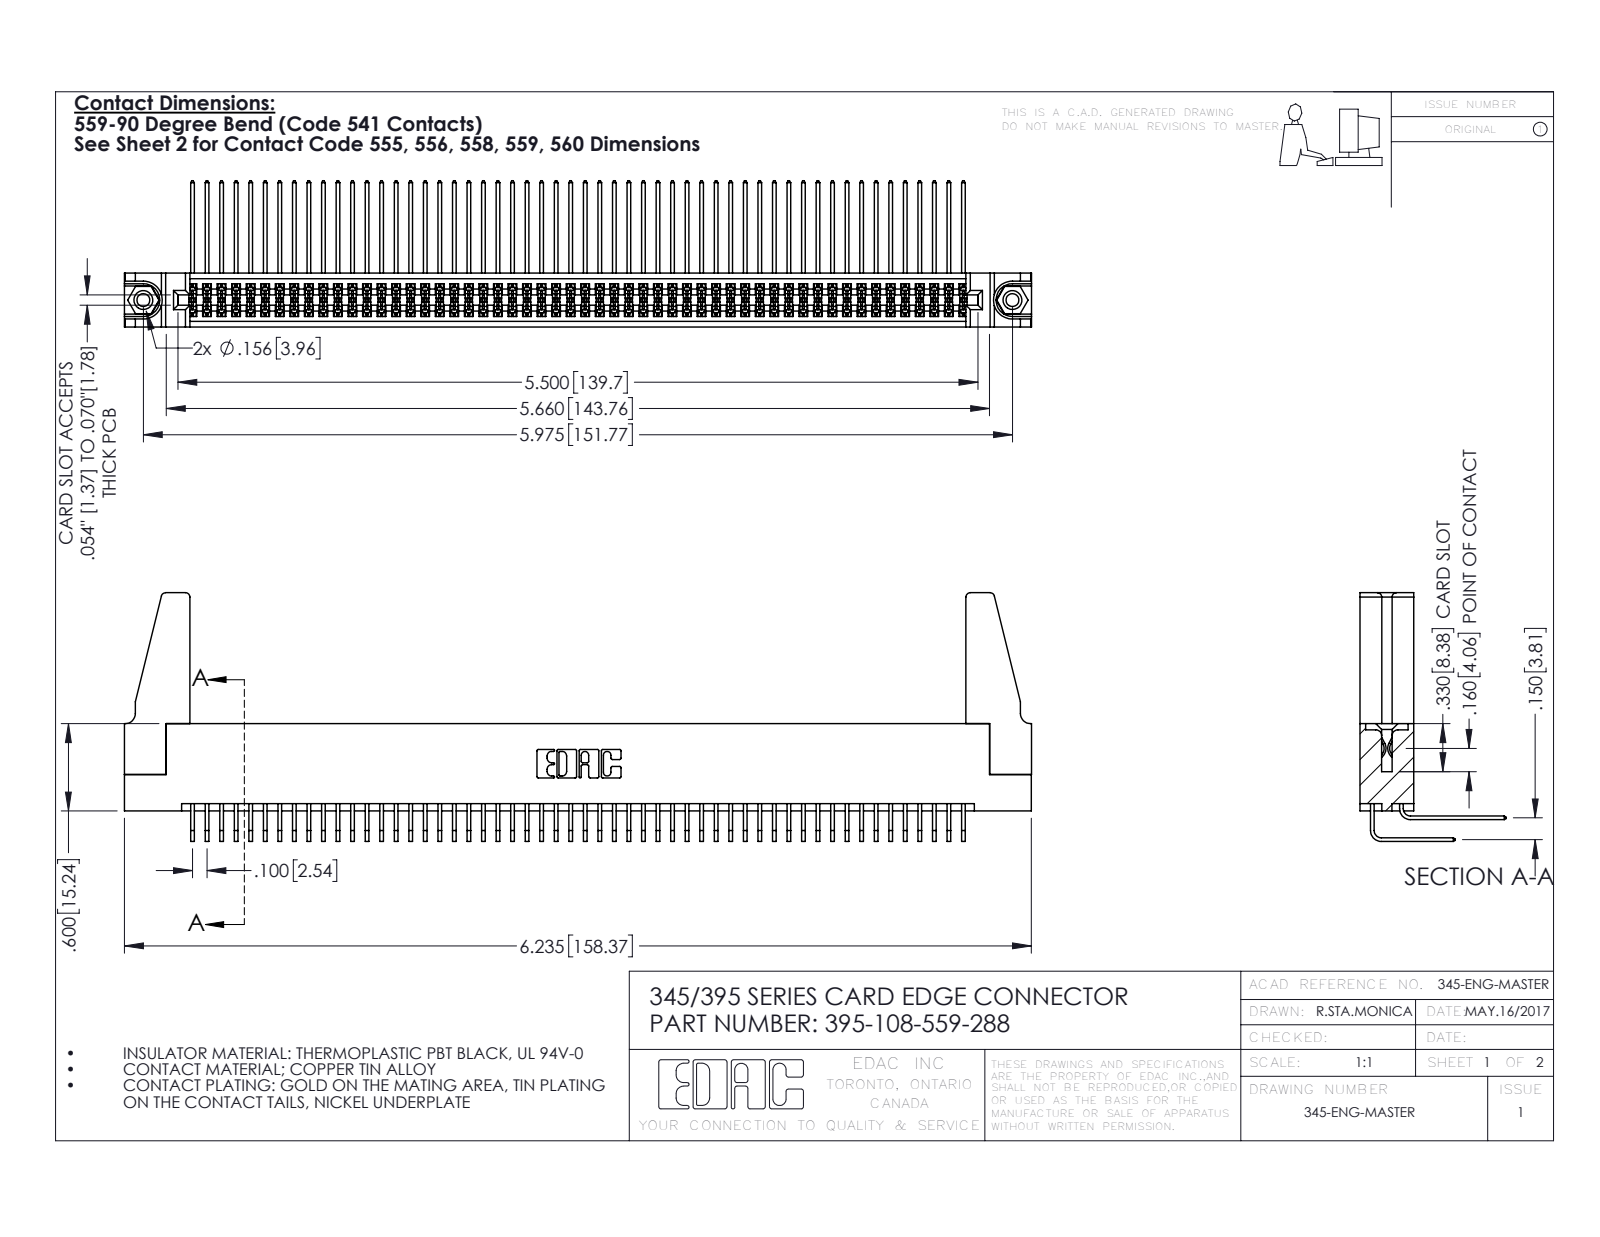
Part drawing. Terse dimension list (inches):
name: 345 Part_Flush Mounting Lugs - 0.156 Dia-TH; 345-220-078_345-220-088; 345-292-001_558 559 Tail - 1; 345-292-001_559 Tail - 2 (+2 more)
written by: SolidWorks 2016 (CONFIG_CONTROL_DESIGN)
unit: in
bodies: 113 solids, 5866 faces (3932 planar, 1918 cylindrical, 16 other)
size: 6.236 × 1.709 × 1.005
volume: 1.182 in³; area: 46.68 in²
holes: 2× ⌀0.089, 2× ⌀0.125, 2× ⌀0.156, 1× ⌀0.064
bosses: 2× ⌀0.155
rounds: 162× R0.006, 22× R0.01, 8× R0.03, 6× R0.007, 6× R0.031, 3× R0.026, 2× R0.014, 2× R0.019
face distances: 0.072, 0.298, 0.37, 0.2, 0.098, 0.272, 0.025, 0.225, 0.175, 0.15
hole spacings: 0.27, 5.739, 5.975
